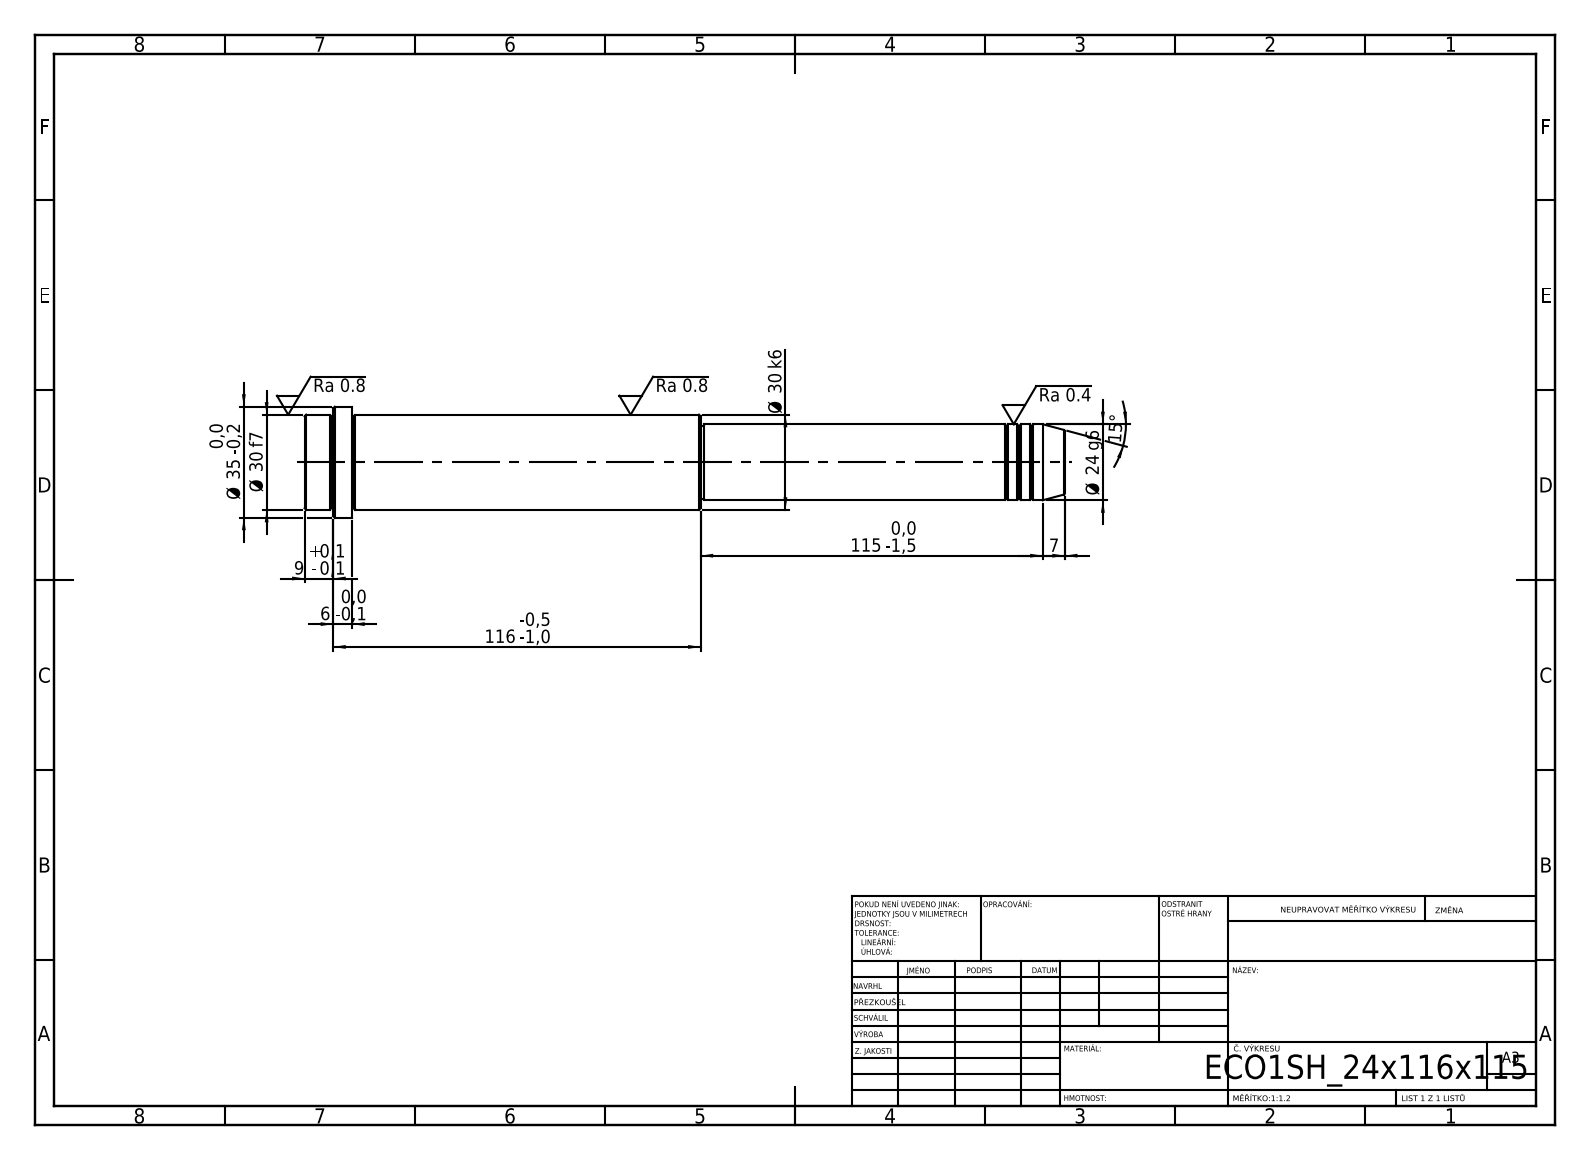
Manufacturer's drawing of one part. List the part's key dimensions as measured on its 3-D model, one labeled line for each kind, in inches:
STEP written by: SolidWorks 2019 (CONFIG_CONTROL_DESIGN)
Units: inches
Bodies: 1 solid, 52 faces (6 planar, 16 cylindrical, 30 other)
Overall size (bounding box): 9.449 × 1.378 × 1.378
Volume: 8.617 in³ · Surface area: 34.89 in²
Round bosses / shafts (diameter × count): ⌀1.378 ×1, ⌀1.181 ×1, ⌀0.945 ×1, ⌀0.906 ×1
Main face-to-face distances: 9.449, 8.858, 0.591, 4.528, 4.331, 4.921, 9.094, 4.567, 0.236, 0.354
